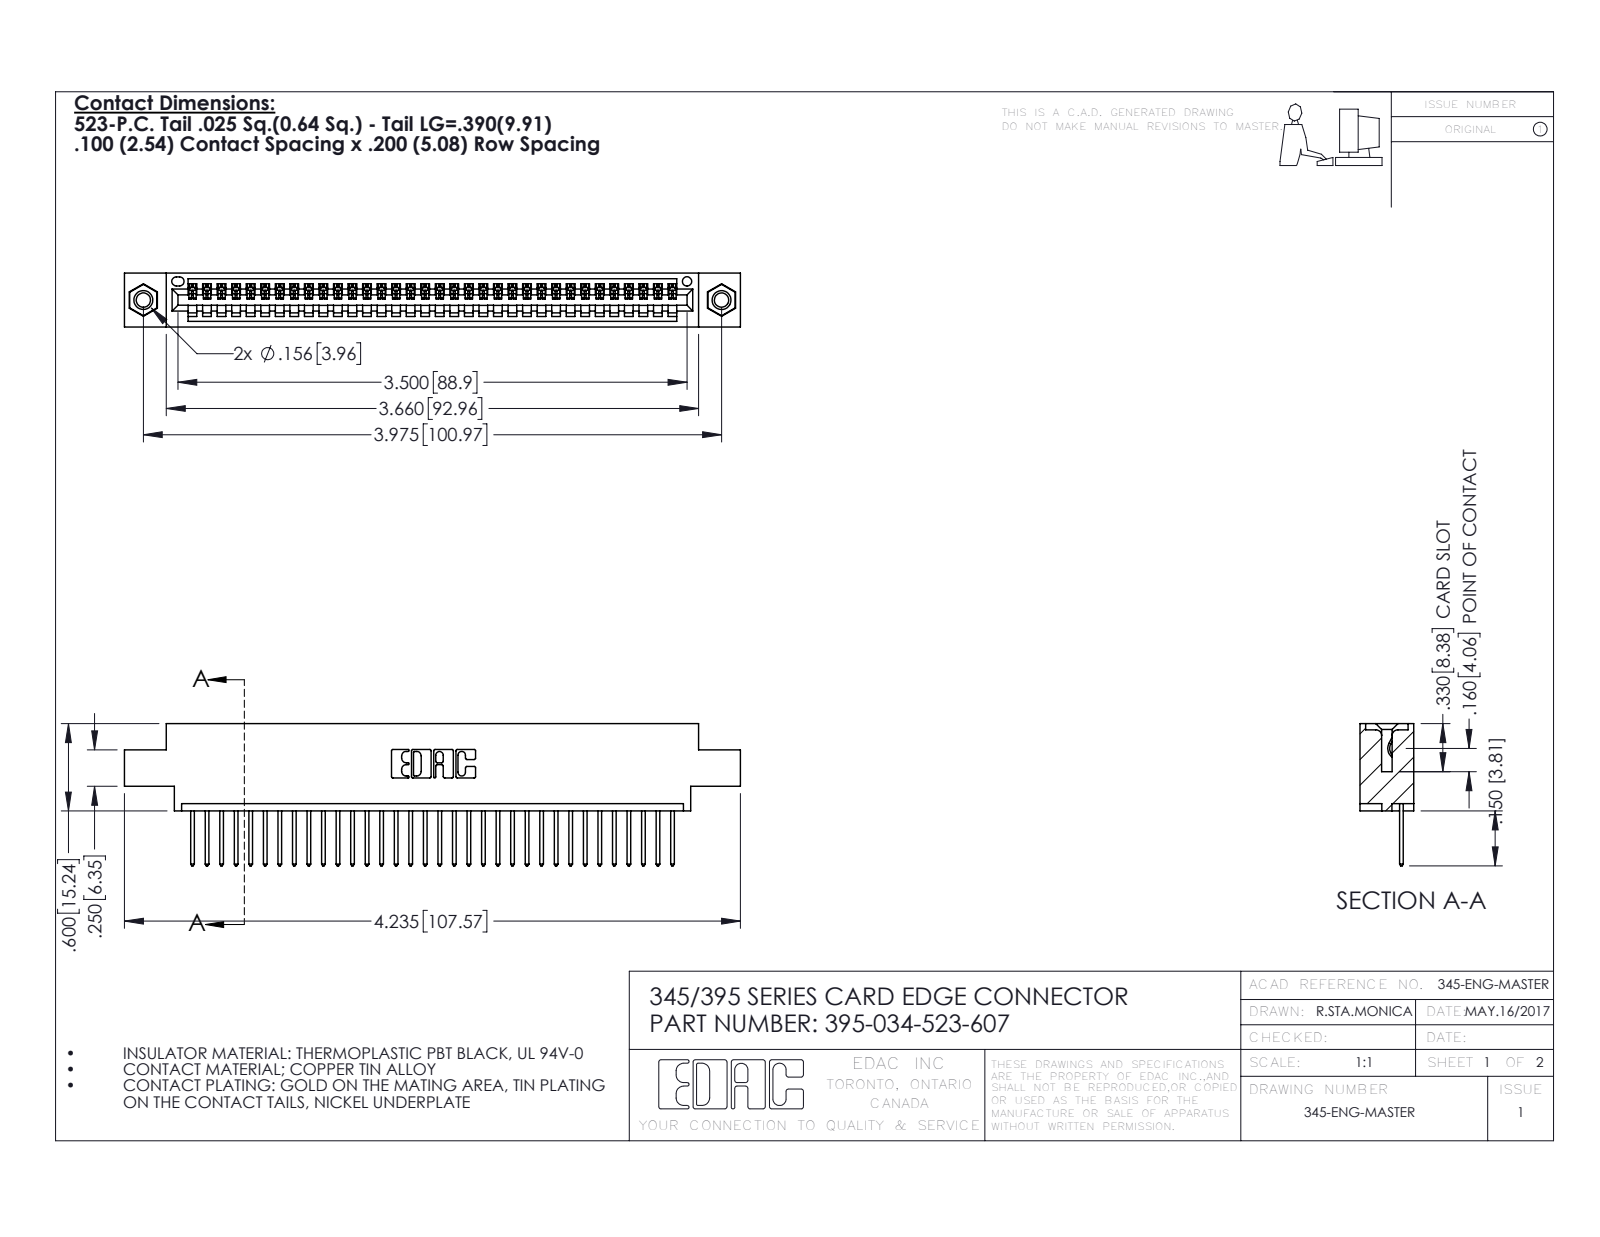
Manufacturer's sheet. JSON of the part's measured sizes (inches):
{"part_name": "395-034-523-607; 345 Part_0.170 Offset - 0.156 Dia-TI; 345-292-001_345-293-123; 345-250-001_345-250-005-103", "step_written_by": "SolidWorks 2016 (CONFIG_CONTROL_DESIGN)", "units": "inches", "bodies": {"solids": 37, "faces": 2162, "planar": 1476, "cylindrical": 670, "other": 16}, "overall_size": [4.235, 0.977, 0.37], "volume_in3": 0.611, "surface_area_in2": 20.76, "round_holes": [[0.098, 2], [0.125, 2], [0.156, 2], [0.064, 1]], "round_bosses_or_shafts": [[0.155, 2]], "partial_cylinders_radius": [[0.006, 68], [0.01, 68], [0.01, 22], [0.007, 6], [0.031, 6], [0.026, 3], [0.031, 2], [0.04, 2]], "face_to_face_distances": [0.072, 0.298, 0.37, 0.2, 0.098, 0.272, 0.025, 0.225, 0.175, 0.149], "hole_center_spacings": [0.27, 3.74, 3.975]}
